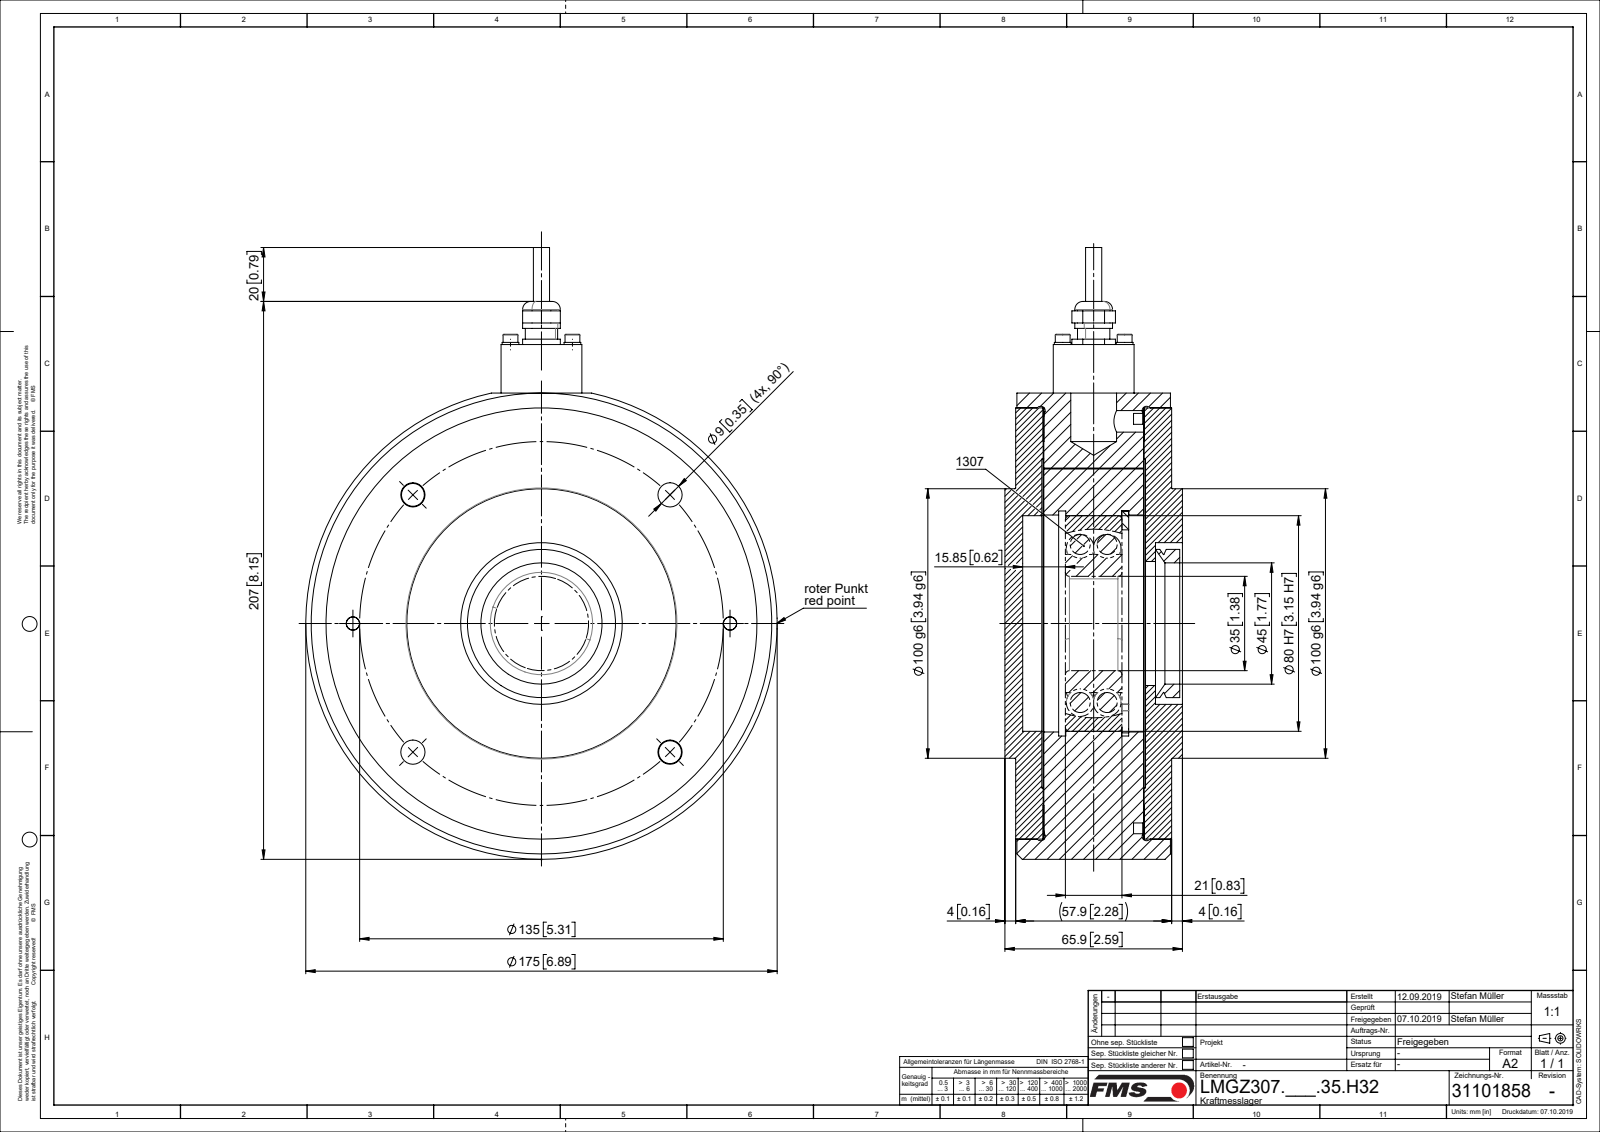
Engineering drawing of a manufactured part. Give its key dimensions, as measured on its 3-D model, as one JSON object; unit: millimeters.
{"part_name": "ZEICHNUNG3; L50006; L4857104; TEIL1 (+8 more)", "step_written_by": "Mechanical Desktop 2009 (CONFIG_CONTROL_DESIGN)", "units": "millimeters", "bodies": {"solids": 22, "faces": 364, "planar": 103, "cylindrical": 203, "other": 58}, "overall_size": [317.5, 207, 104.7], "volume_mm3": 1263000, "surface_area_mm2": 264334, "round_holes": [[2.6, 4], [3.2, 4], [3.4, 4], [9, 4], [5, 2], [6.6, 2], [8.68, 2], [11, 2], [6, 1], [8, 1], [10, 1], [11.28, 1]], "round_bosses_or_shafts": [[6.2, 4], [5.5, 4], [3, 4], [10, 2], [6, 2], [175, 1], [160, 1], [100, 1]], "partial_cylinders_radius": [[7.5, 2]], "face_to_face_distances": [37.25, 10.2, 10.45, 47.45, 47.7, 37, 9.7, 48.2, 0.5, 0.75], "hole_center_spacings": [16.26, 23, 48.72, 52.67, 67.5, 95.46, 115.55, 127.04]}
